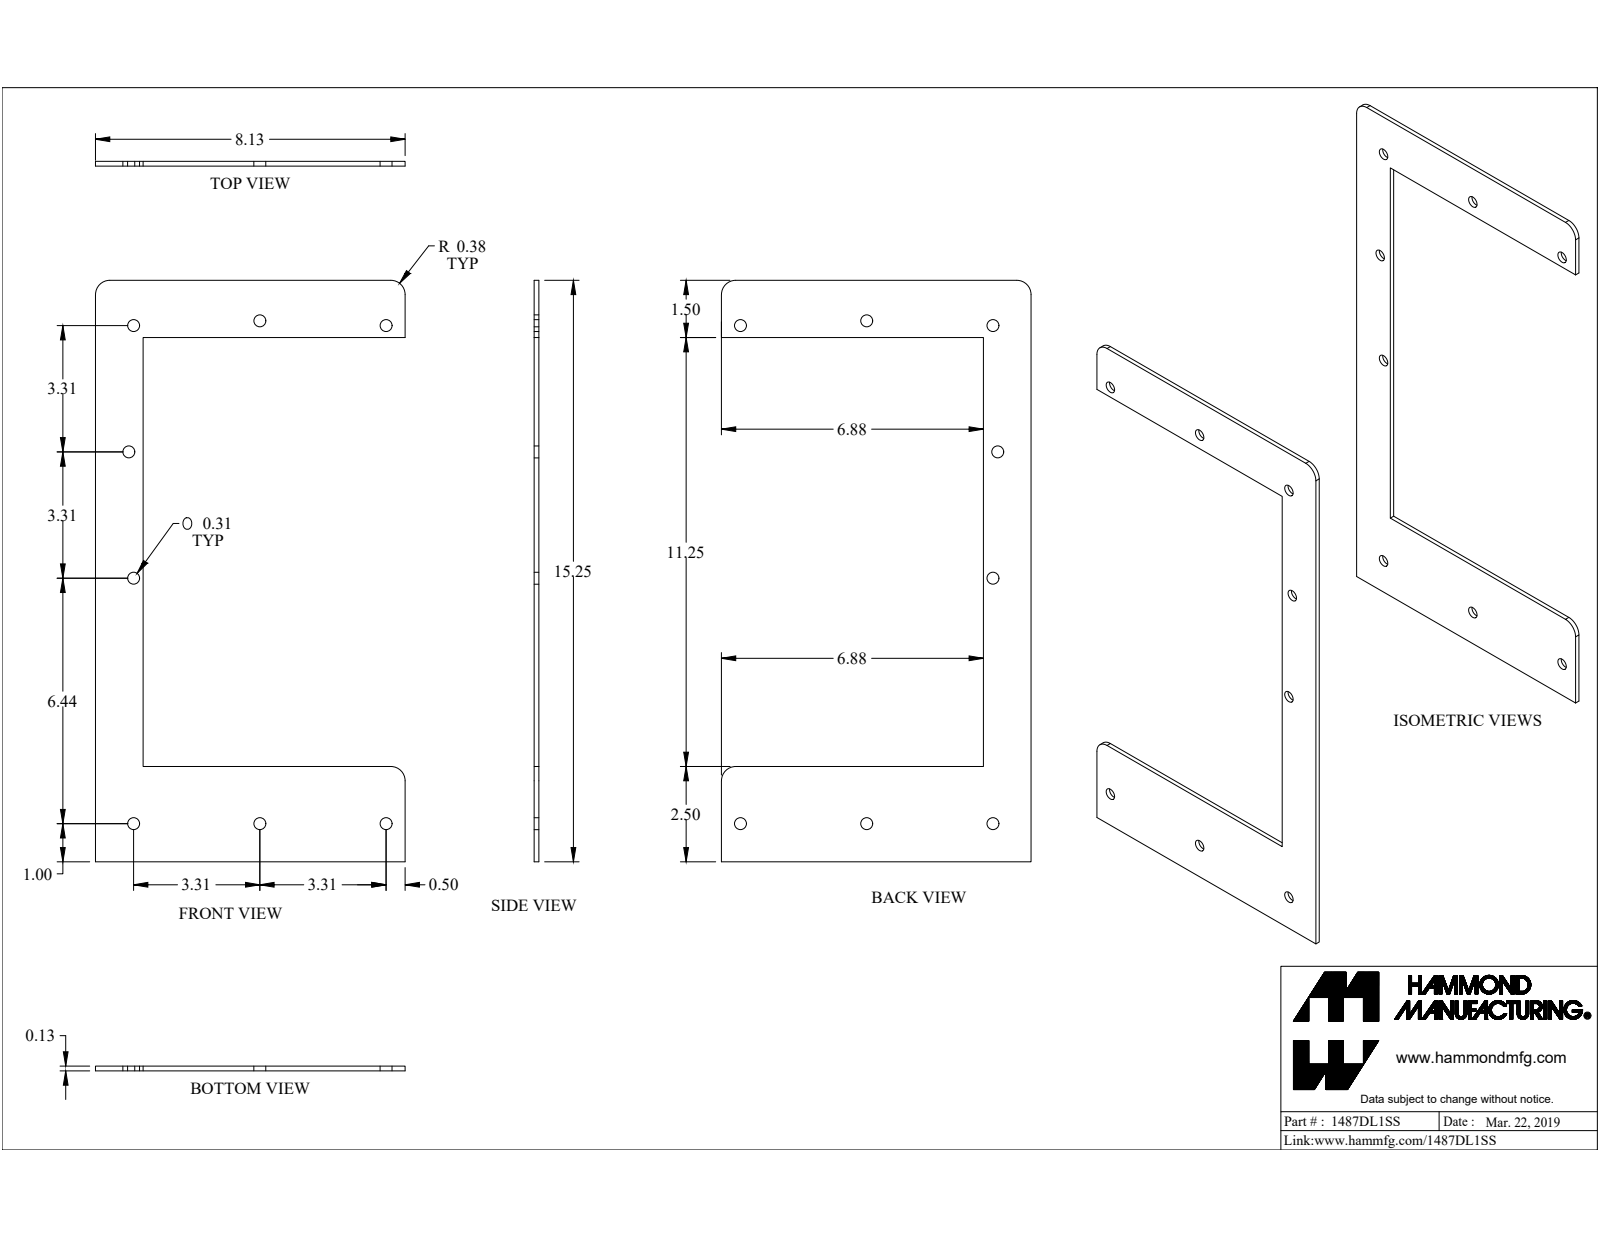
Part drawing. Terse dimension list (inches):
name: 1487DL1SS
written by: SolidWorks 2019 (CONFIG_CONTROL_DESIGN)
unit: in
bodies: 6 solids, 226 faces (144 planar, 47 cylindrical, 35 other)
size: 15.5 × 10.125 × 2.971
volume: 6.232 in³; area: 124.8 in²
holes: 8× ⌀0.313, 1× ⌀0.196, 1× ⌀0.258, 1× ⌀0.35
bosses: 1× ⌀0.5, 1× ⌀0.25
rounds: 7× R0.375, 6× R0.02, 1× R0.25
face distances: 0.125, 0.03, 1.25, 15.28, 15.25, 2.5, 1.5, 1.53, 13.75, 12.78
hole spacings: 3.315, 6.625, 3.313, 7.519, 13.063, 13.476, 13.597, 14.647
